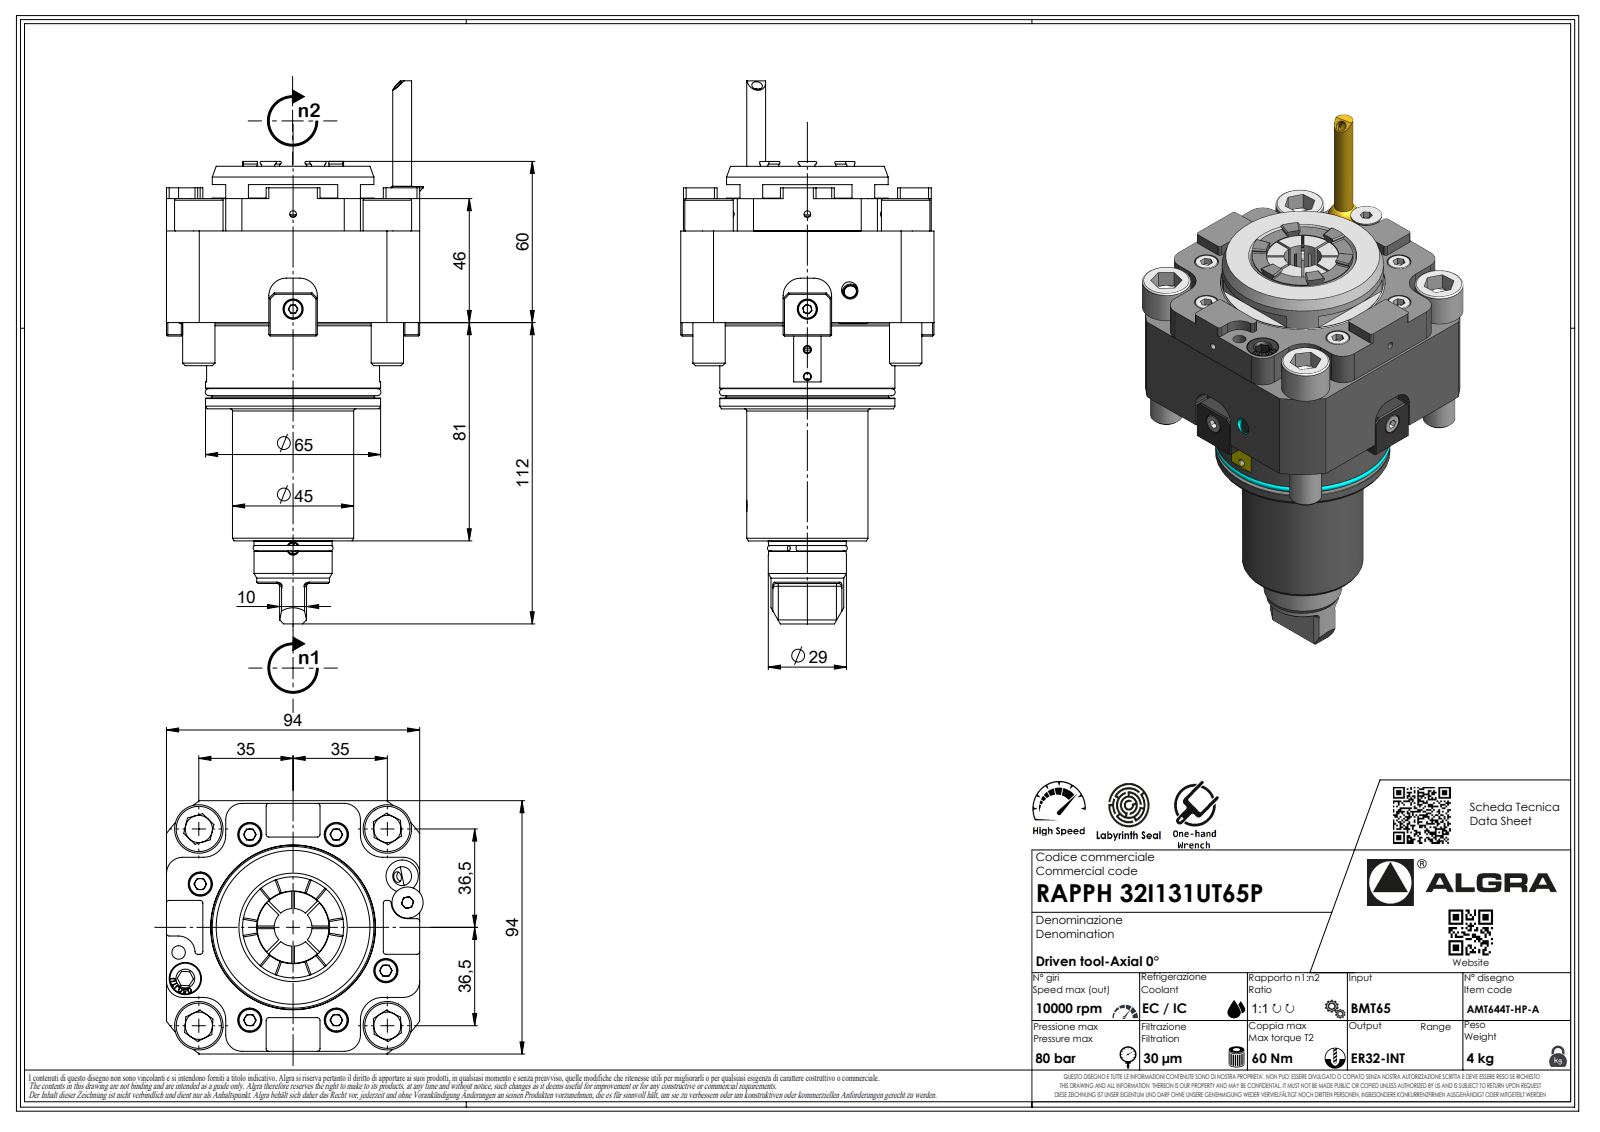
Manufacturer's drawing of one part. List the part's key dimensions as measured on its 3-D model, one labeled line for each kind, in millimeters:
Part name (STEP PRODUCT): RAPPH32I131UT65P
STEP written by: SolidWorks 2023 (AUTOMOTIVE_DESIGN)
Units: millimetres
Bodies: 1 solid, 658 faces (417 planar, 104 cylindrical, 137 other)
Overall size (bounding box): 171.61 × 94 × 94
Volume: 624 366 mm³ · Surface area: 61 027 mm²
Round holes (diameter × count): ⌀2.1 ×1, ⌀27 ×1
Round bosses / shafts (diameter × count): ⌀18 ×4, ⌀12 ×4, ⌀65 ×1, ⌀60.3 ×1, ⌀60 ×1, ⌀45 ×1, ⌀29 ×1, ⌀6.37 ×1
Partial cylindrical surfaces — rounded edges, fillets, slot ends (radius × count): R1 ×24, R6 ×8, R0.33 ×7, R0.52 ×7, R3.7 ×7, R6.5 ×4, R8.25 ×4, R6.1 ×2
Main face-to-face distances: 94, 46, 12, 16, 58, 50, 78, 32, 66, 1
